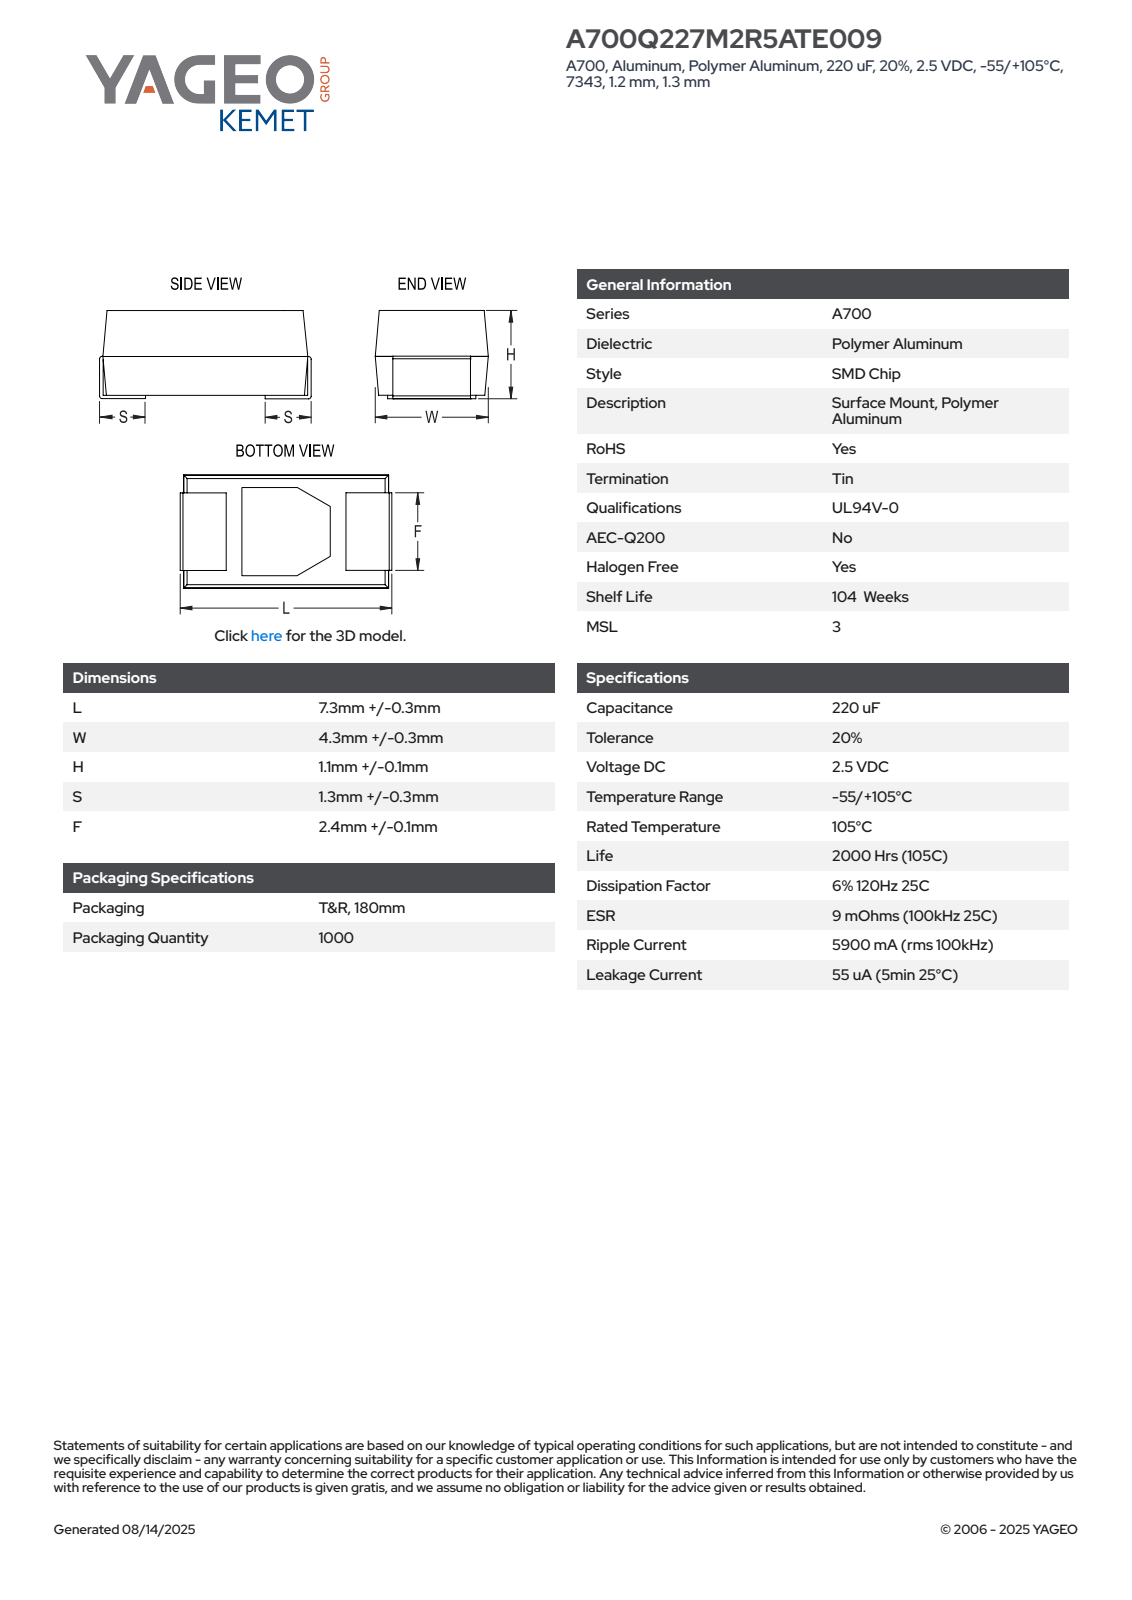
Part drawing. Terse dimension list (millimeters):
name: CAS_SMD_L7.6W4.6H1.2S1.3F2.5
written by: SolidWorks 2021 (AUTOMOTIVE_DESIGN)
unit: mm
bodies: 1 solid, 82 faces (78 planar, 4 cylindrical, 0 other)
size: 7.6 × 4.6 × 1.21
volume: 36 mm³; area: 98 mm²
rounds: 4× R0.1
face distances: 1.1, 1.2, 4.32, 4.33, 7.5, 6.74, 6.73, 7.4, 7.6, 1.64
